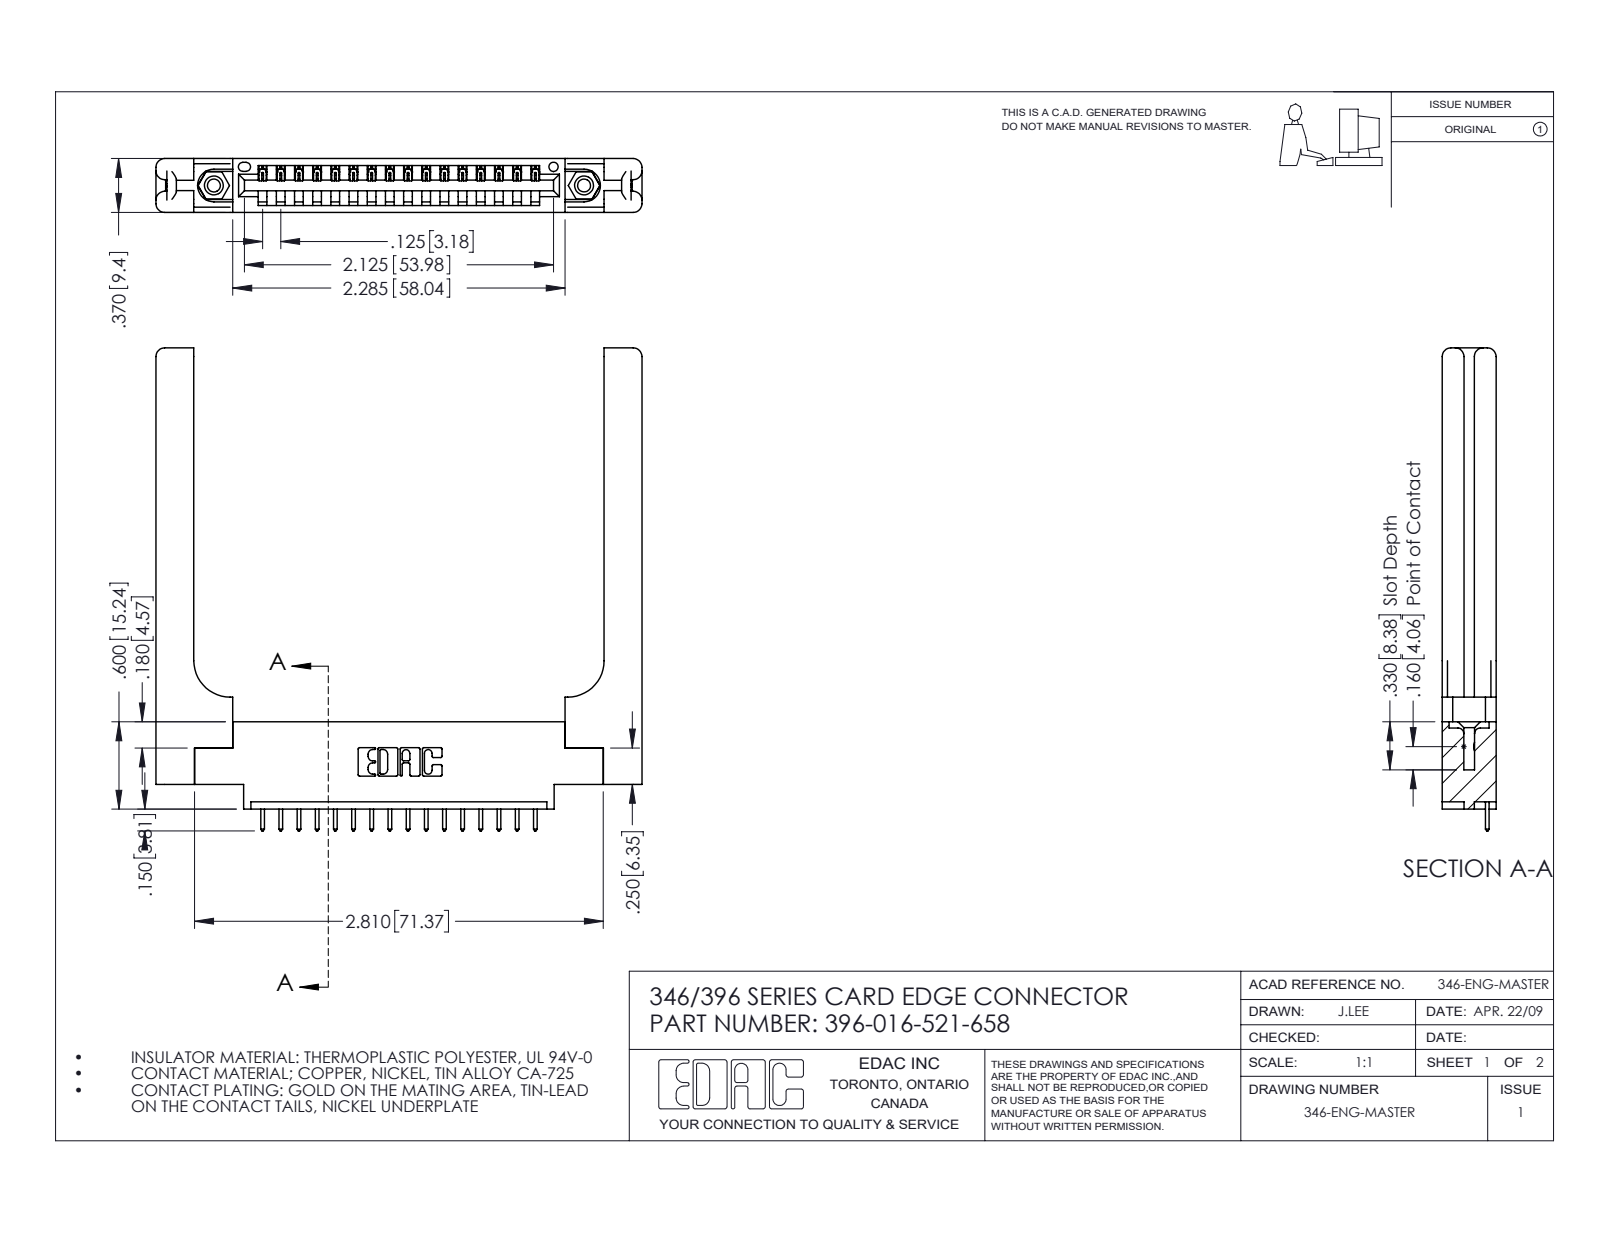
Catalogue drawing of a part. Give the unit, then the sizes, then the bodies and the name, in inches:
Units: inches
Overall size (bounding box): 3.341 × 3.32 × 0.37
Round holes (diameter × count): ⌀0.089 ×2, ⌀0.125 ×2, ⌀0.156 ×2, ⌀0.064 ×1
Round bosses / shafts (diameter × count): ⌀0.155 ×2
Partial cylindrical surfaces — rounded edges, fillets, slot ends (radius × count): R0.006 ×32, R0.01 ×32, R0.01 ×22, R0.06 ×16, R0.007 ×6, R0.031 ×6, R0.026 ×3, R0.03 ×2
Main face-to-face distances: 0.37, 0.15, 0.072, 0.148, 0.048, 0.322, 0.25, 0.102, 0.22, 0.173
Hole centre spacings: 0.246, 2.338, 2.545
Volume: 0.931 in³ · Surface area: 22.55 in²
Bodies: 21 solids, 1310 faces (868 planar, 382 cylindrical, 60 other)
Part name (STEP PRODUCT): 346-220-058_345-220-058; 345-250-001_345-250-001-102; 396-016-521-658; 346 Part_0.170 Offset - 0.156 Dia-TH (+1 more)
STEP written by: SolidWorks 2016 (CONFIG_CONTROL_DESIGN)
